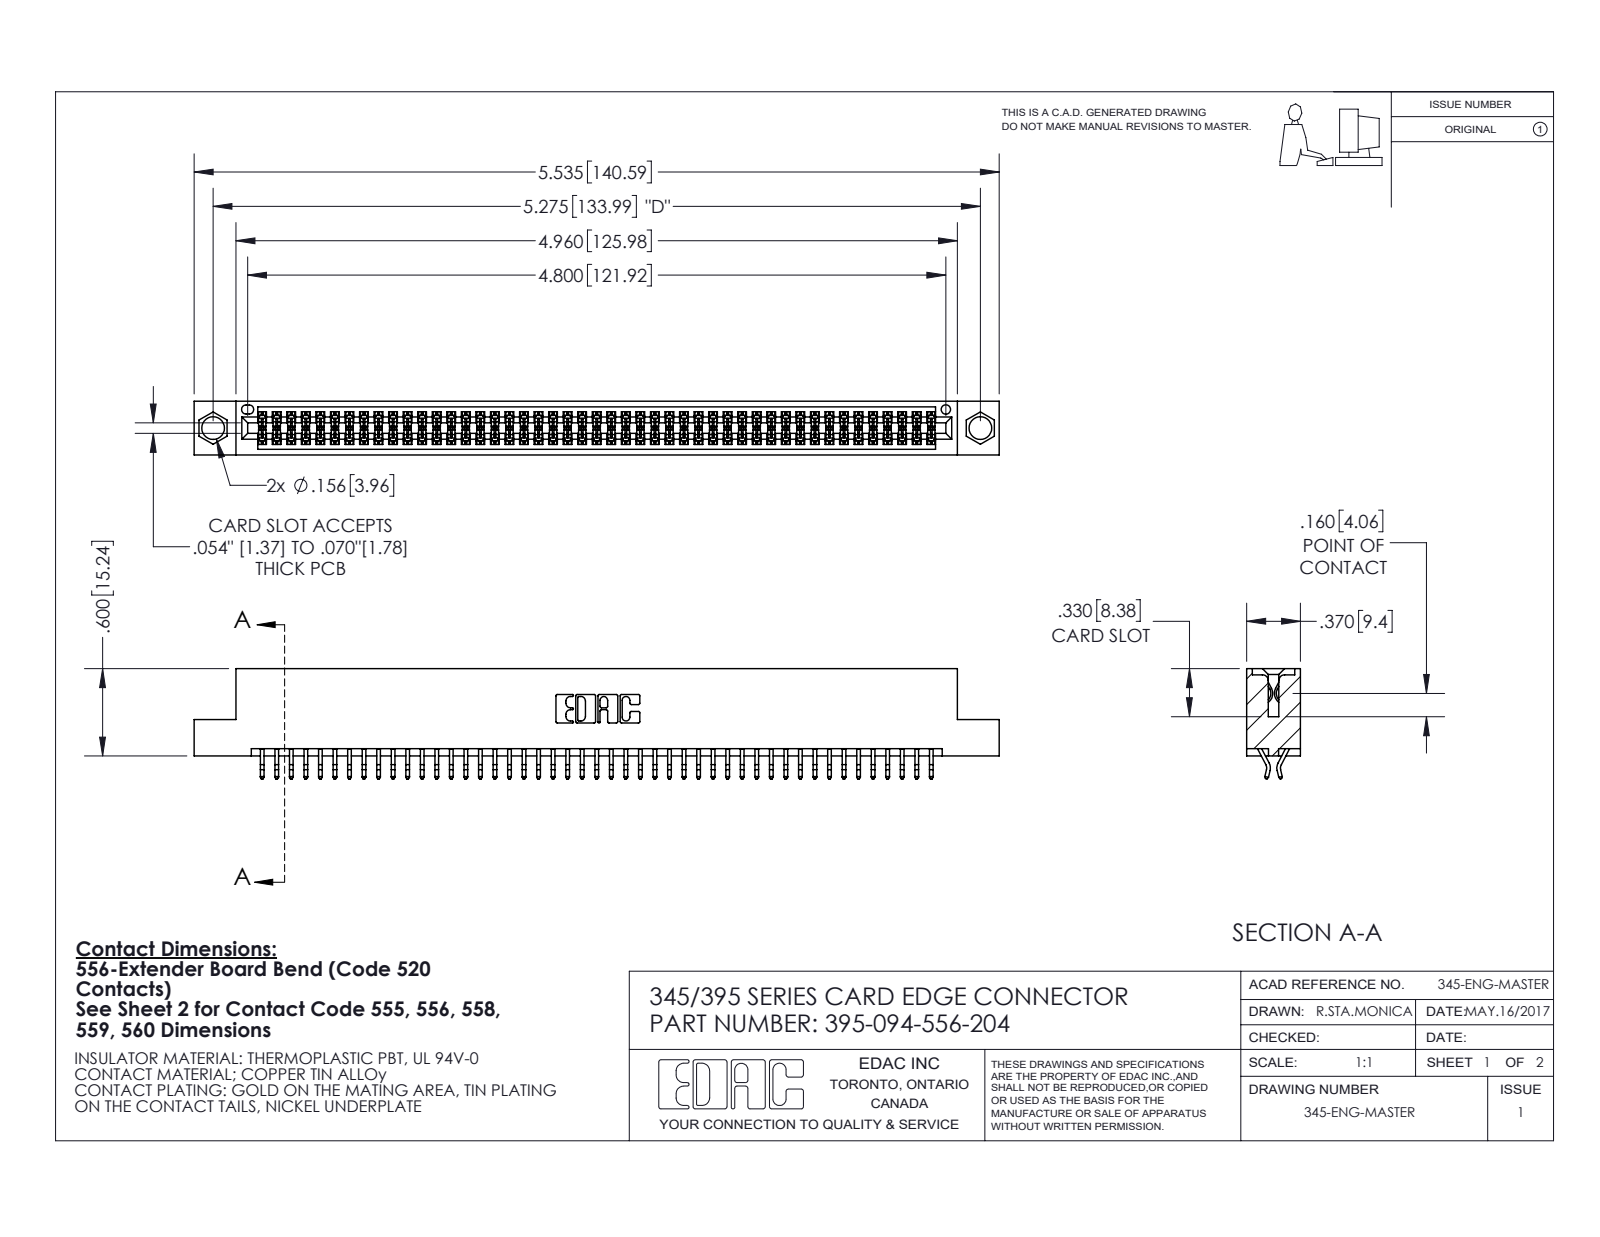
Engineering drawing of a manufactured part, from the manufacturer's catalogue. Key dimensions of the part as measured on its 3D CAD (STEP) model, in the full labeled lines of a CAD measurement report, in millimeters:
Part name (STEP PRODUCT): 345-292-001_556 Tail; 395-094-556-204; 345 Part_Flush Mounting Lugs - 0.156 Dia-TI
STEP written by: SolidWorks 2020 (CONFIG_CONTROL_DESIGN)
Units: millimetres
Bodies: 95 solids, 5404 faces (3572 planar, 1832 cylindrical, 0 other)
Overall size (bounding box): 140.6 × 19.2 × 9.4
Volume: 13 600 mm³ · Surface area: 19 960 mm²
Round holes (diameter × count): ⌀4 ×2, ⌀1.6 ×1
Partial cylindrical surfaces — rounded edges, fillets, slot ends (radius × count): R0.2 ×188, R0.3 ×22, R0.2 ×6, R0.8 ×6, R0.7 ×3, R0.3 ×2, R0.4 ×2, R0.5 ×2
Main face-to-face distances: 7.6, 1.8, 5.1, 9.4, 0.6, 2.5, 6.9, 5.7, 4.4, 3.8
Hole centre spacings: 6.9, 128, 134
